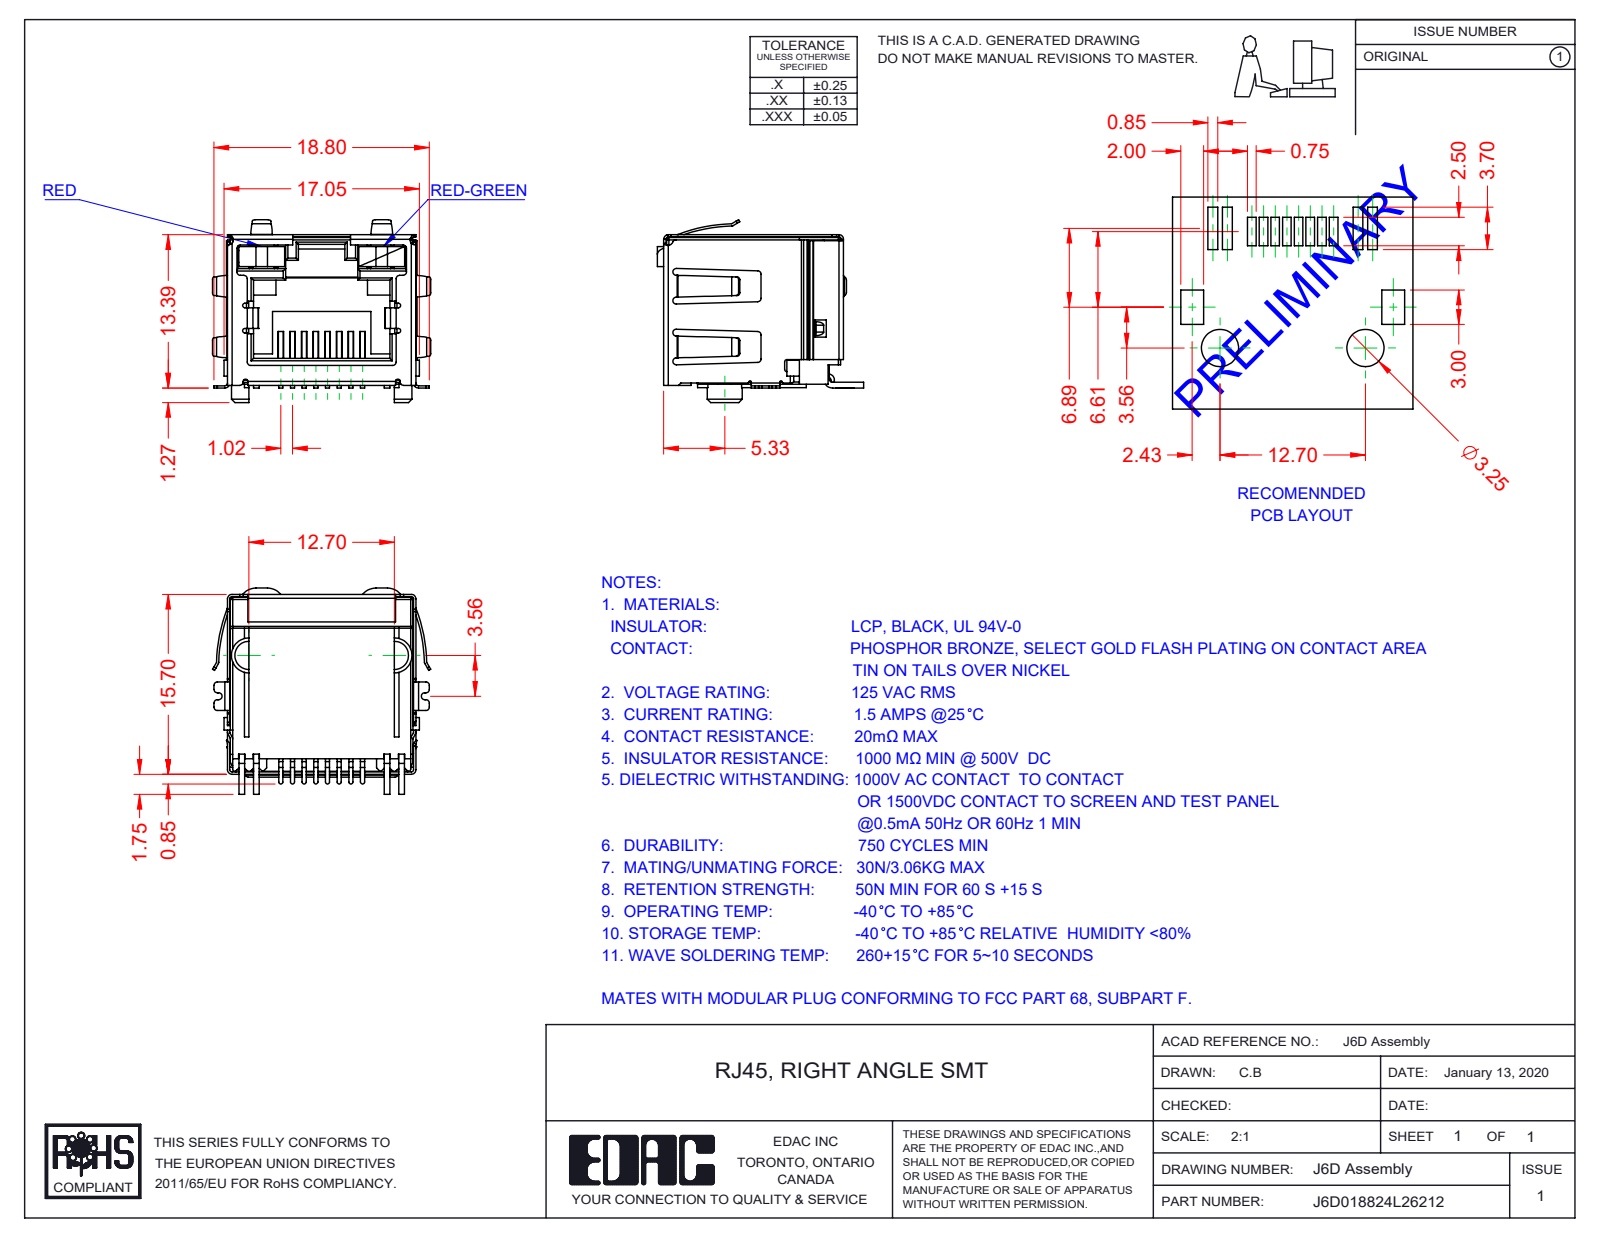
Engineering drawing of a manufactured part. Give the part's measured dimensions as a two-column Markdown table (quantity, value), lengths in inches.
| quantity | value |
| --- | --- |
| part name | 6D Insulator; J6D018824L26212; 6D LED RH_6-Red-Green; 6D Contacts (+2 more) |
| STEP written by | SolidWorks 2016 (CONFIG_CONTROL_DESIGN) |
| units | inches |
| bodies | 12 solids, 1031 faces (702 planar, 284 cylindrical, 45 other) |
| overall size | 0.75 × 0.709 × 0.628 |
| volume | 0.109 in³ |
| surface area | 7.434 in² |
| partial cylindrical surfaces (radius × count) | 0.012 × 55, 0.008 × 40, 0.016 × 19, 0.01 × 16, 0.004 × 12, 0.006 × 8, 0.007 × 8, 0.02 × 6 |
| main face-to-face distances | 0.63, 0.638, 0.64, 0.089, 0.039, 0.628, 0.504, 0.018, 0.514, 0.417 |
